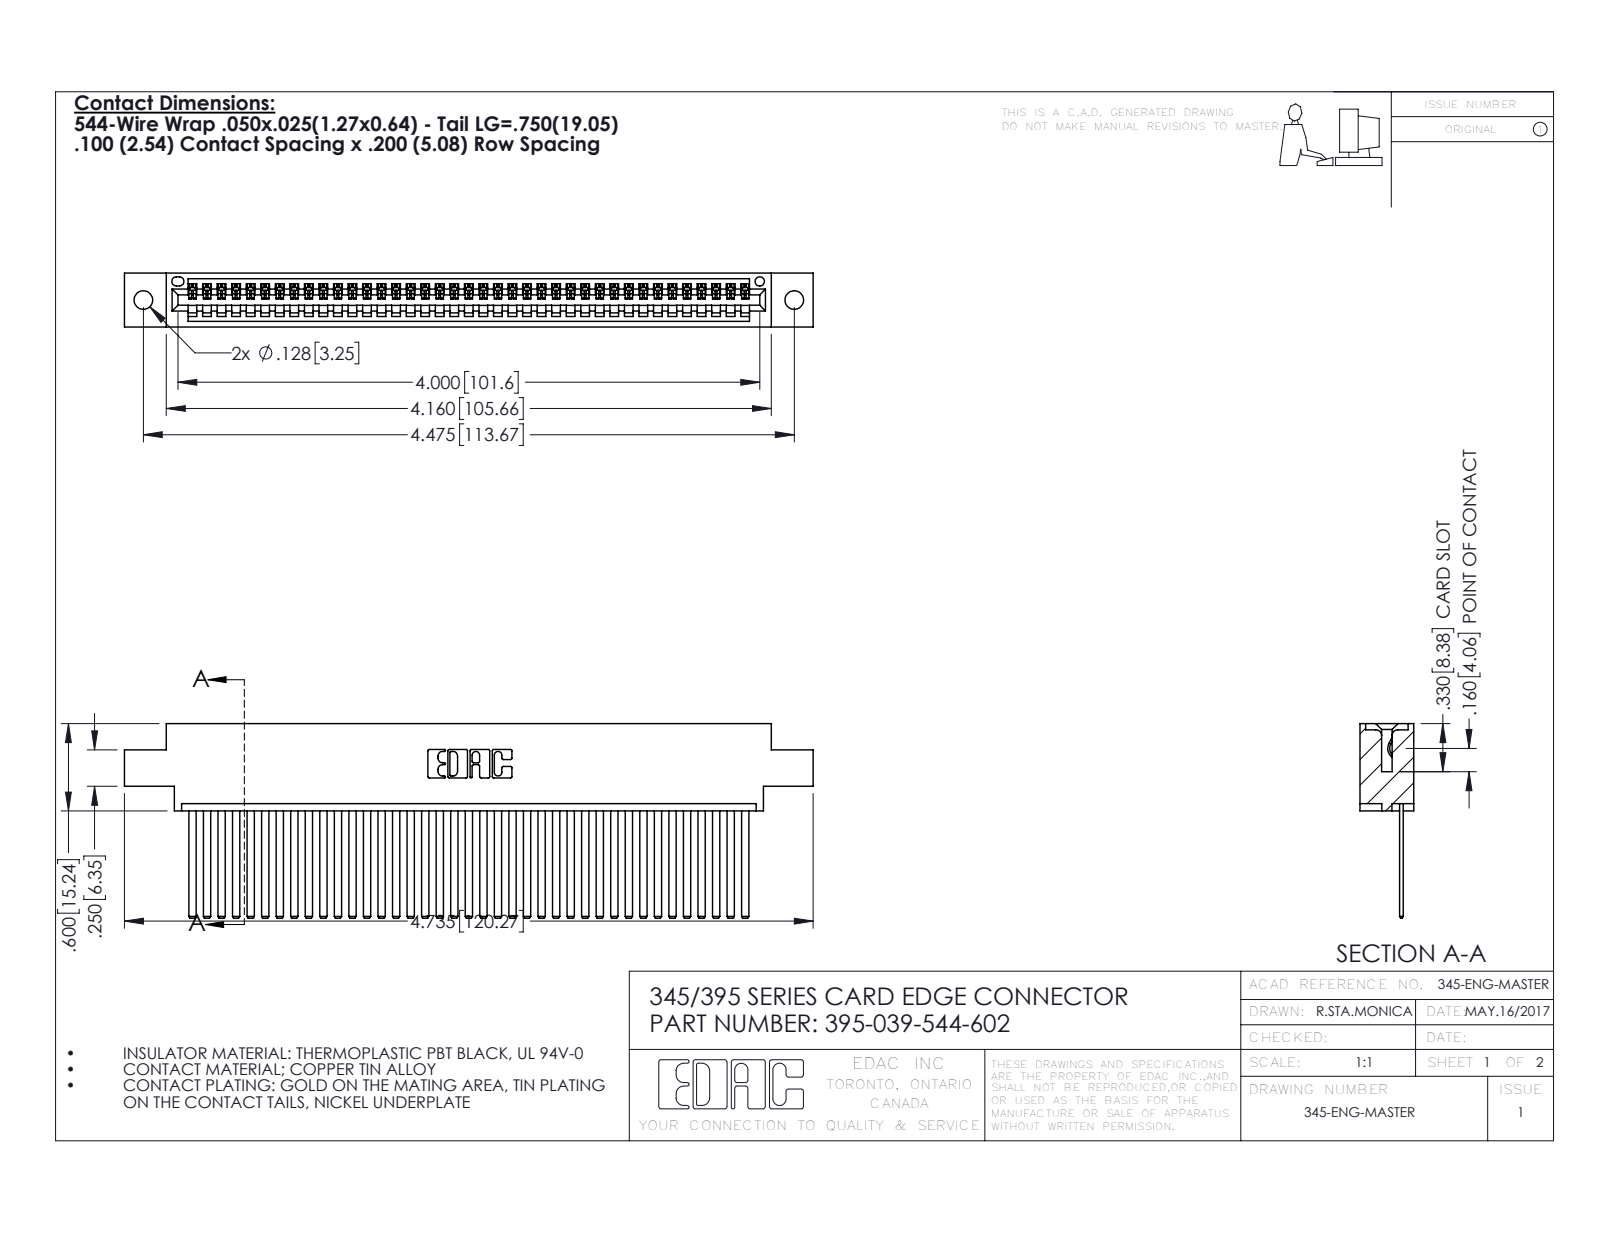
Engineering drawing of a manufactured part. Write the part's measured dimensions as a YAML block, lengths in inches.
part_name: "395-039-544-602; 345 Part_0.170 Offset - 0.128 Dia; 345-292-001_345-293-144"
step_written_by: "SolidWorks 2016 (CONFIG_CONTROL_DESIGN)"
units: inches
bodies: {solids: 40, faces: 2158, planar: 1488, cylindrical: 670, other: 0}
overall_size: [4.735, 1.337, 0.37]
volume: 0.714
surface_area: 25.91
round_holes:
  - {diameter: 0.128, count: 2}
  - {diameter: 0.064, count: 1}
partial_cylinders:
  - {radius: 0.006, count: 78}
  - {radius: 0.01, count: 22}
  - {radius: 0.007, count: 6}
  - {radius: 0.031, count: 6}
  - {radius: 0.026, count: 3}
  - {radius: 0.031, count: 2}
  - {radius: 0.04, count: 2}
  - {radius: 0.014, count: 1}
face_to_face_distances: [0.072, 0.298, 0.025, 0.098, 0.272, 0.37, 0.2, 0.225, 0.175, 0.149]
hole_center_spacings: [0.27, 4.239, 4.475]
